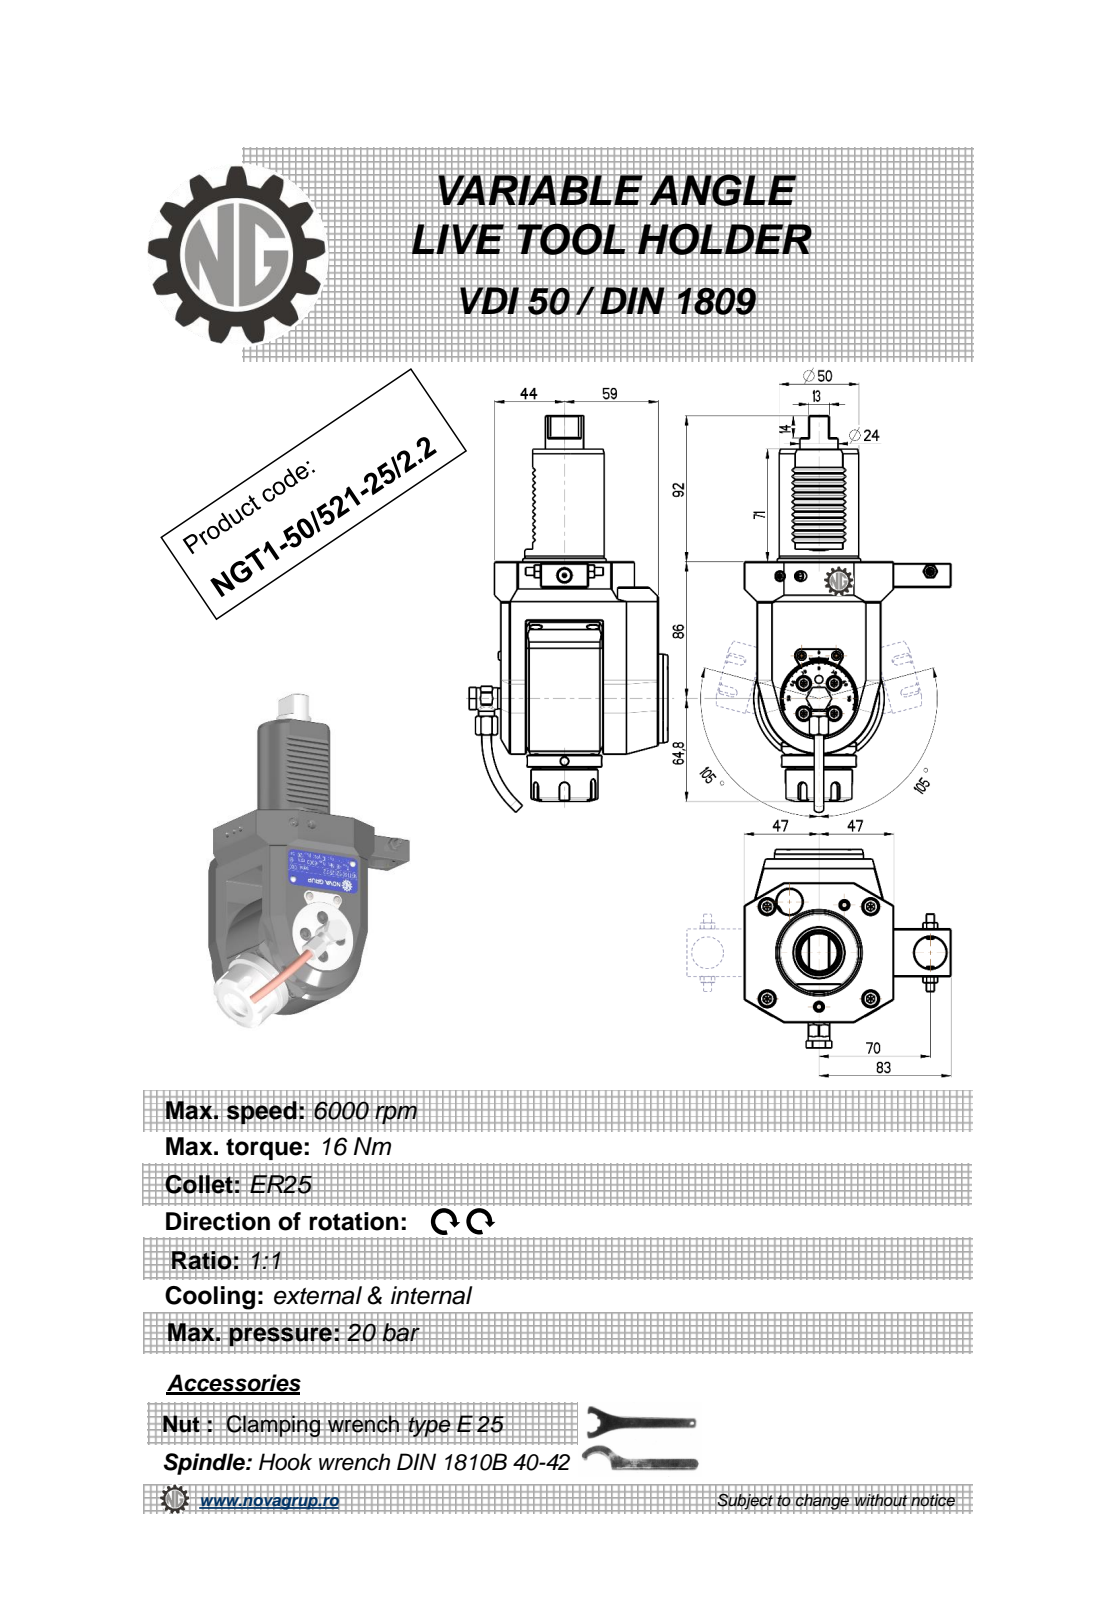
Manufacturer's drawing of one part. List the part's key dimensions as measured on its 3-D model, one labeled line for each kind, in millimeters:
Part name (STEP PRODUCT): NGT1_50_521_25_2_2
STEP written by: PRO/ENGINEER BY PARAMETRIC TECHNOLOGY CORPORATION, 2010280 (CONFIG_CONTROL_DESIGN)
Units: millimetres
Bodies: 1 solid, 604 faces (271 planar, 140 cylindrical, 193 other)
Overall size (bounding box): 249.67 × 130 × 124.9
Volume: 1 032 000 mm³ · Surface area: 91 342 mm²
Round holes (diameter × count): ⌀4 ×3, ⌀5 ×2, ⌀3 ×1, ⌀6.2 ×1, ⌀9 ×1, ⌀9.5 ×1, ⌀10 ×1, ⌀11 ×1, ⌀20 ×1, ⌀20.3 ×1
Round bosses / shafts (diameter × count): ⌀6 ×2, ⌀5.7 ×2, ⌀56 ×1, ⌀50 ×1, ⌀47 ×1, ⌀42 ×1, ⌀35 ×1, ⌀24 ×1
Partial cylindrical surfaces — rounded edges, fillets, slot ends (radius × count): R0.26 ×12, R0.3 ×12, R0.16 ×6, R3 ×5, R0.5 ×4, R0.8 ×2, R1 ×2, R10 ×2
Main face-to-face distances: 37, 99, 16, 21, 8, 6, 64, 105, 20, 78
Hole centre spacings: 0.4, 39.45, 49, 49.4, 70, 85.45, 85.68, 116.95
